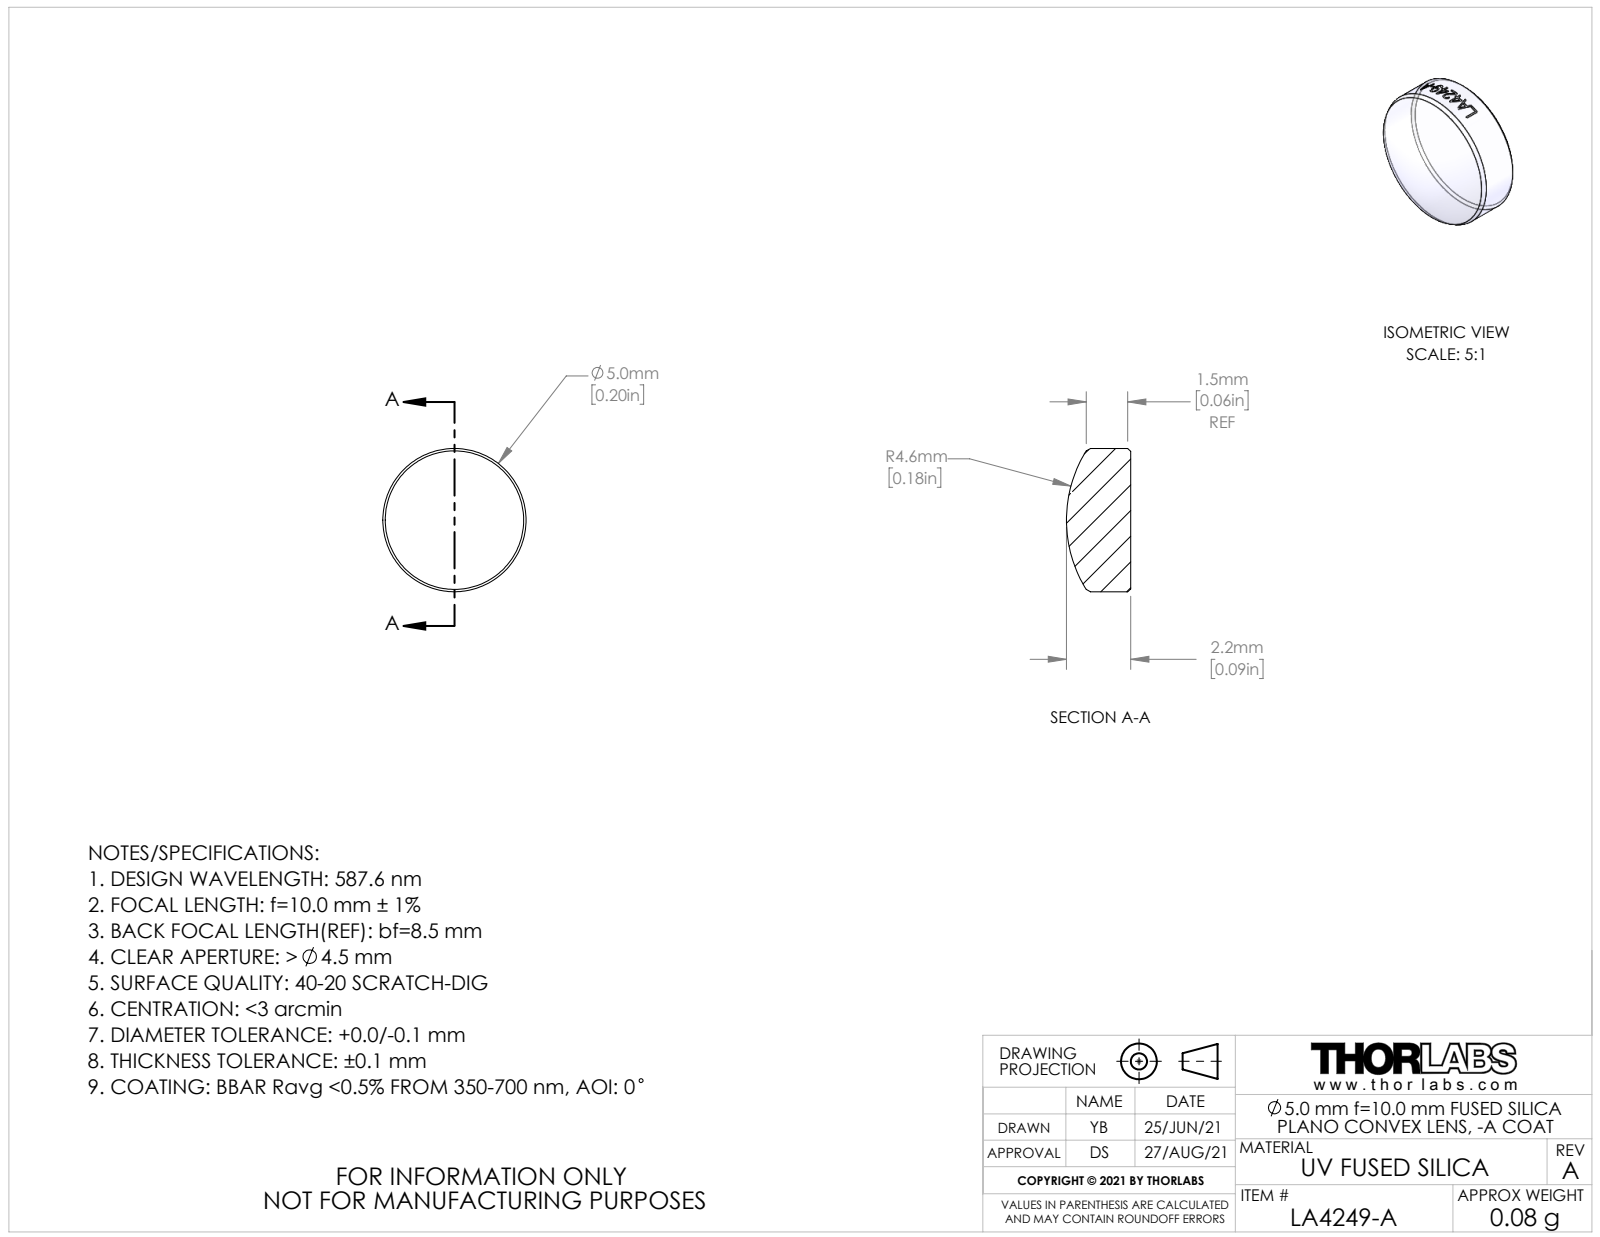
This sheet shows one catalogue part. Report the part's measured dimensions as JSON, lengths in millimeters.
{"part_name": "CTN017506-E0W; CTN017549", "step_written_by": "SolidWorks 2018 (AUTOMOTIVE_DESIGN)", "units": "millimeters", "bodies": {"solids": 1, "faces": 22, "planar": 1, "cylindrical": 15, "other": 6}, "overall_size": [5, 5, 2.24], "volume_mm3": 37, "surface_area_mm2": 63, "round_bosses_or_shafts": [[5, 1]]}
